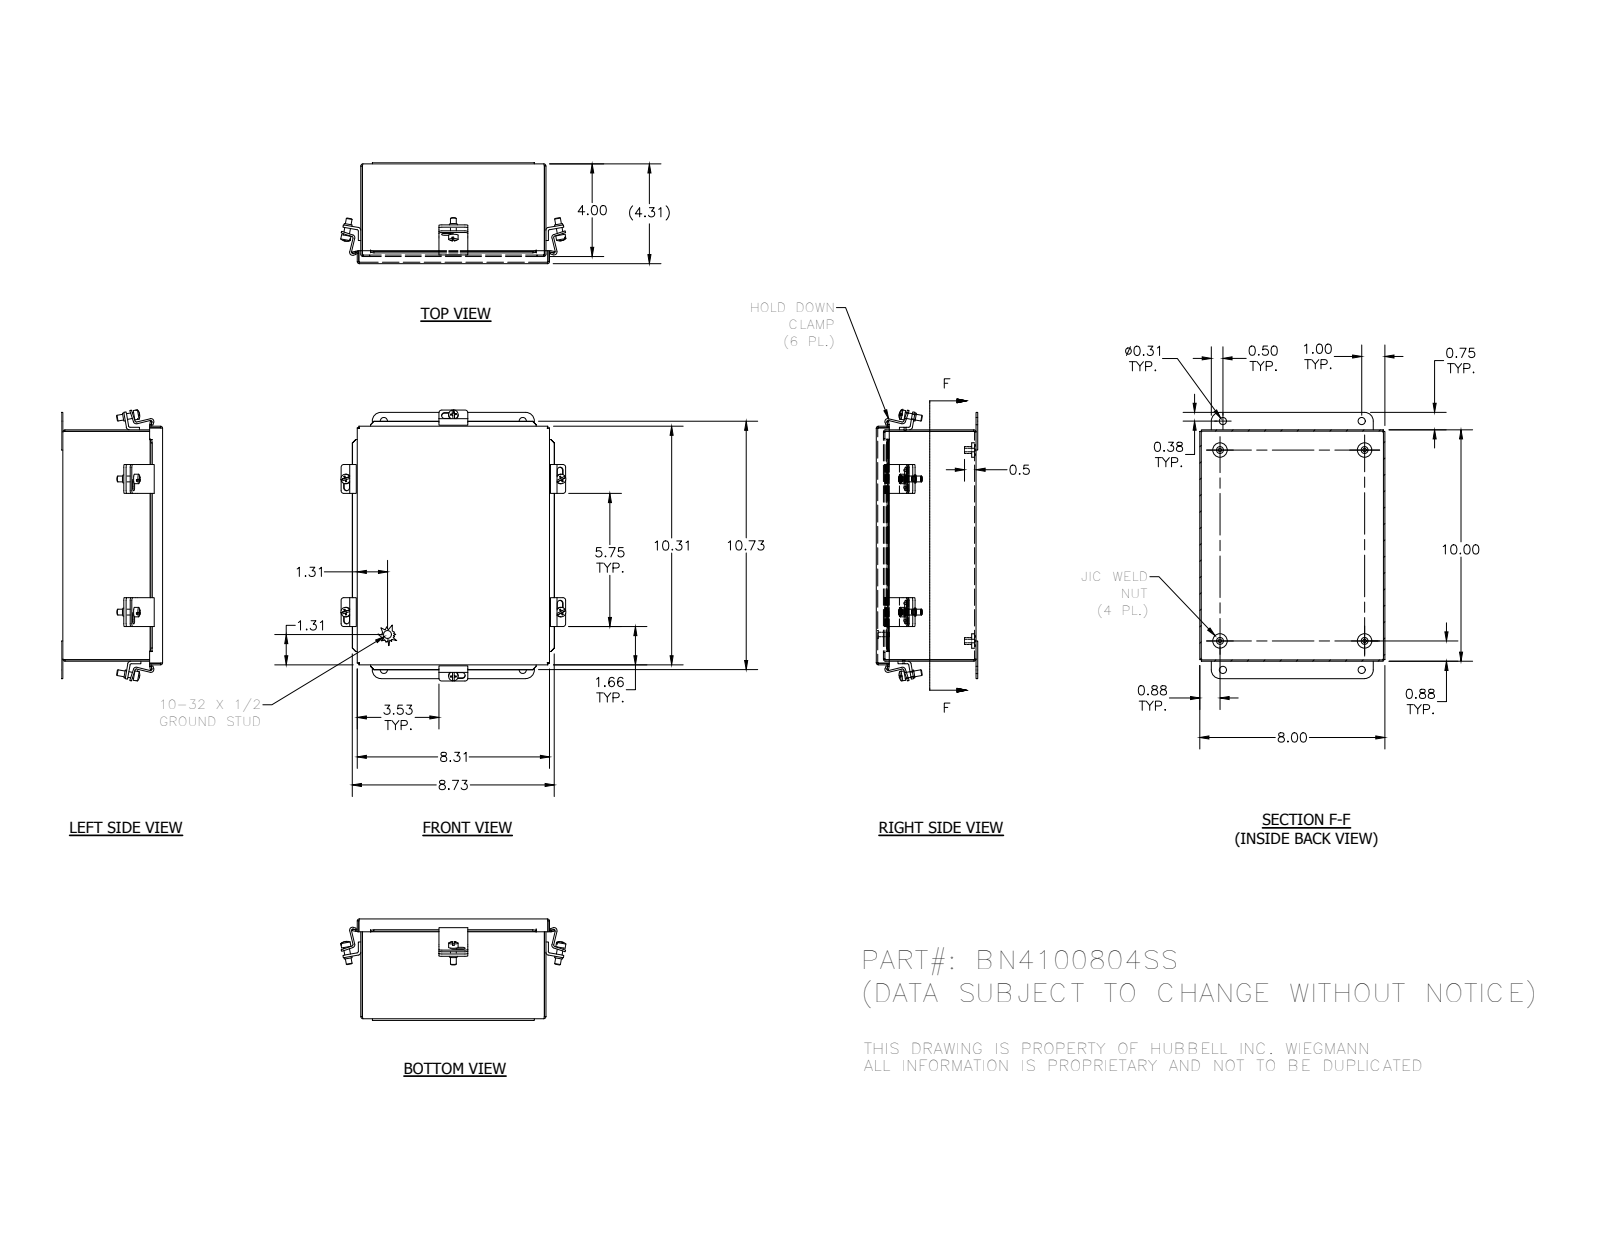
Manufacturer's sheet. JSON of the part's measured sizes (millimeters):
{"part_name": "C2002_1; 34854_1; BN4100804SS; BN41008SSLID_1 (+5 more)", "step_written_by": "SolidWorks 2014 (AUTOMOTIVE_DESIGN)", "units": "millimeters", "bodies": {"solids": 27, "faces": 753, "planar": 363, "cylindrical": 264, "other": 126}, "overall_size": [297.5, 247, 111.5], "volume_mm3": 411500, "surface_area_mm2": 508500, "round_holes": [[2.8, 8], [5, 6], [4, 4], [7.9, 4]], "round_bosses_or_shafts": [[10.4, 6], [8.7, 6], [6.4, 6], [15.9, 4], [7.6, 4], [8.6, 1], [4.8, 1]], "partial_cylinders_radius": [[3.2, 24], [0.8, 16], [2.4, 16], [1.6, 12], [3.2, 12], [3.4, 12], [9.5, 4]], "face_to_face_distances": [1.6, 108, 109.6, 106.3, 201.6, 252.4, 203.2, 200, 254, 250.8], "hole_center_spacings": [19.1, 31.9, 146.1, 241.3, 1.6, 19.1, 152.4, 158.8]}
